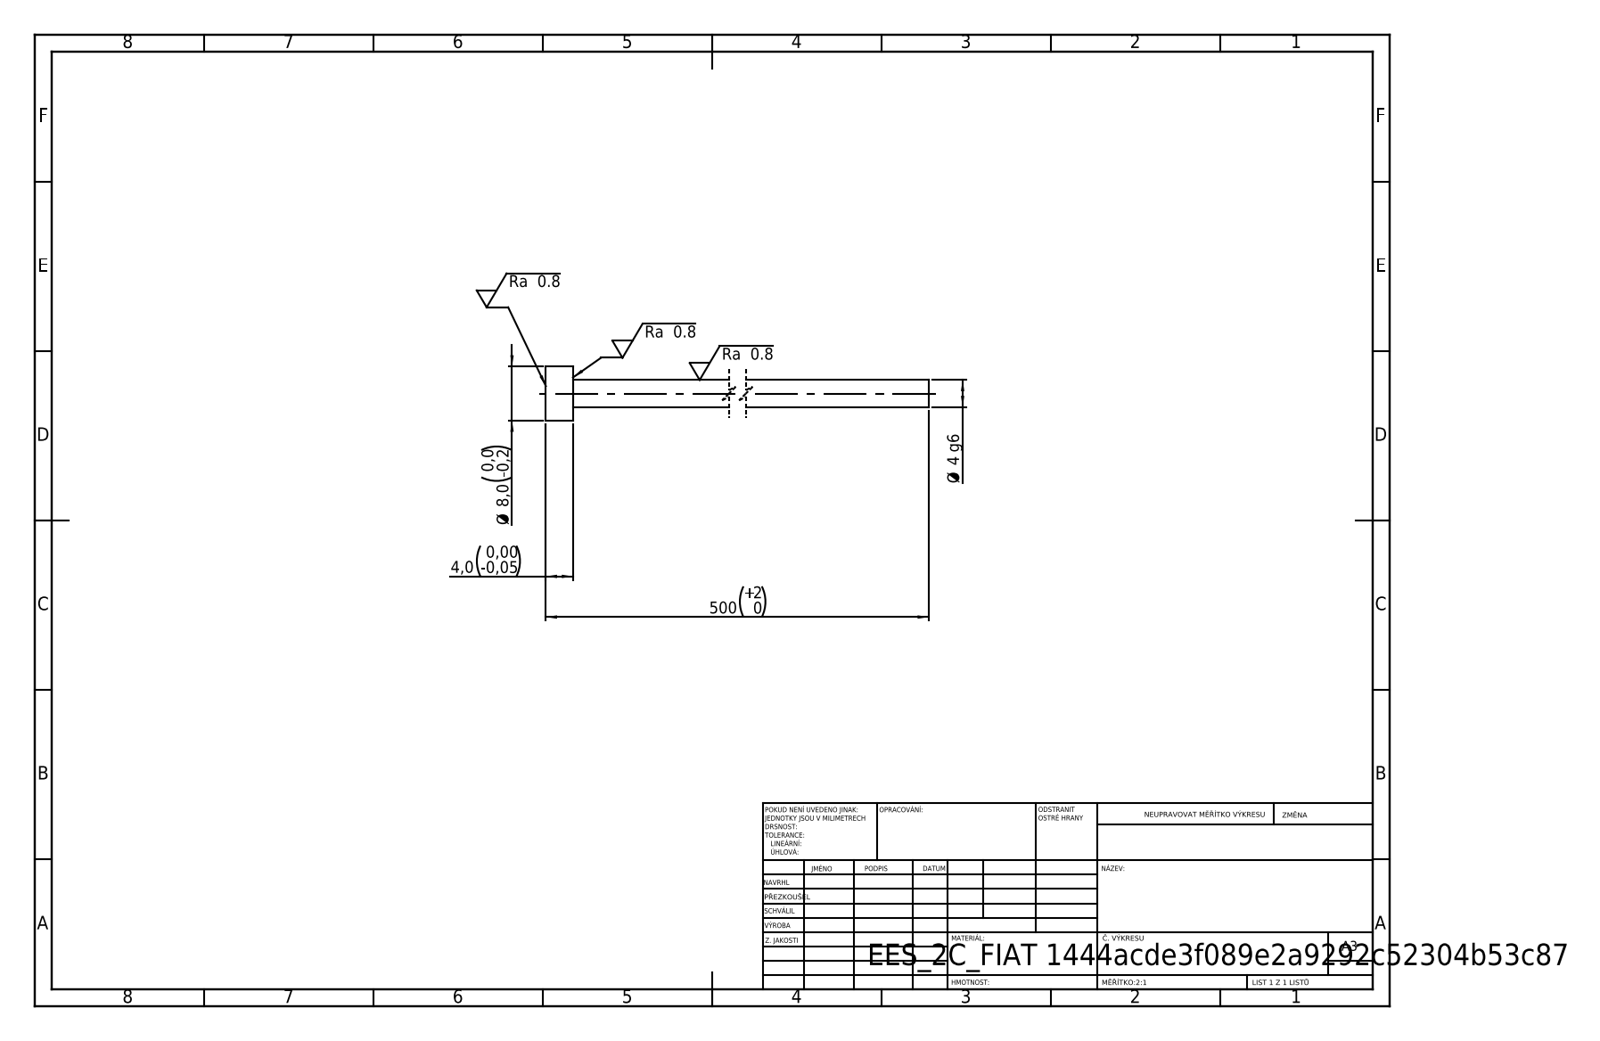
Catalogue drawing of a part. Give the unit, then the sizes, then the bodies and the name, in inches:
Units: inches
Overall size (bounding box): 19.685 × 0.315 × 0.315
Round bosses / shafts (diameter × count): ⌀0.315 ×1, ⌀0.157 ×1
Main face-to-face distances: 0.157, 19.685, 19.528
Volume: 0.393 in³ · Surface area: 9.973 in²
Bodies: 1 solid, 7 faces (3 planar, 4 cylindrical, 0 other)
STEP written by: SolidWorks 2019 (CONFIG_CONTROL_DESIGN)
